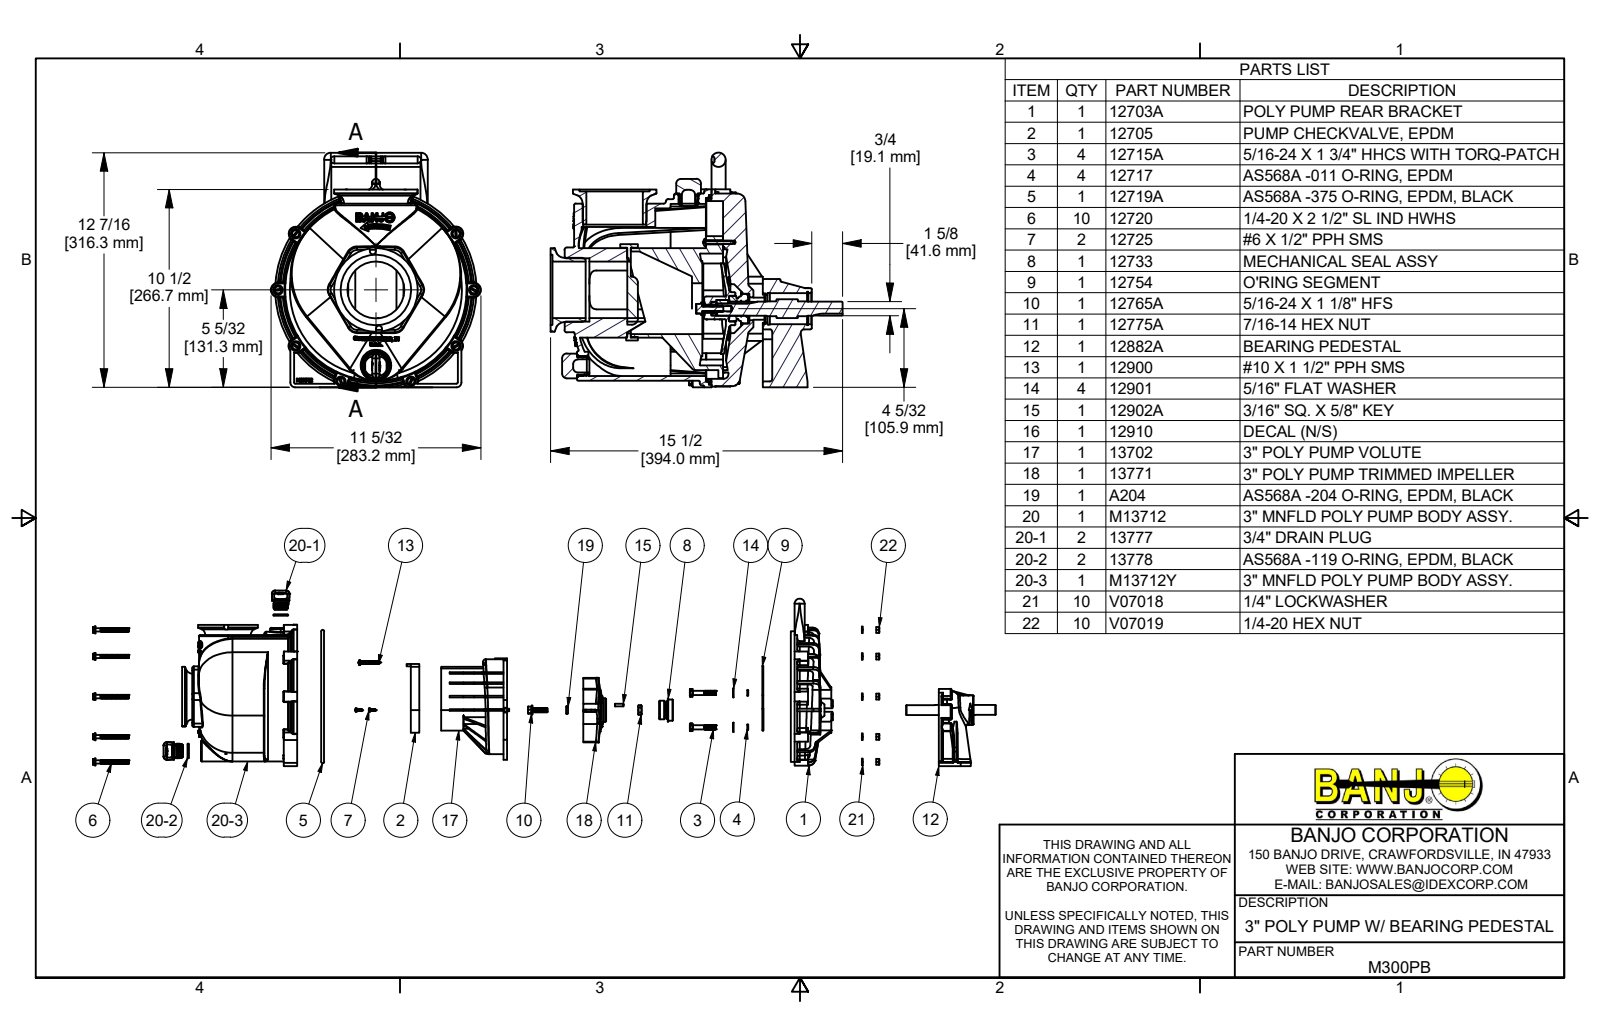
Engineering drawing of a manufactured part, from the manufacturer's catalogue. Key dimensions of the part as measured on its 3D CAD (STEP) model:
Part name (STEP PRODUCT): M300PB; 12703A; 12715A; 12717 (+8 more)
STEP written by: Autodesk Inventor 2019 (AUTOMOTIVE_DESIGN)
Units: inches
Bodies: 55 solids, 4980 faces (816 planar, 1578 cylindrical, 2586 other)
Overall size (bounding box): 12.417 × 11.15 × 4.35
Volume: 66.25 in³ · Surface area: 675 in²
Round holes (diameter × count): ⌀0.196 ×10, ⌀0.252 ×10, ⌀0.27 ×10, ⌀0.344 ×4, ⌀0.469 ×4, ⌀0.815 ×4, ⌀0.115 ×2, ⌀0.205 ×2, ⌀0.18 ×1, ⌀0.375 ×1, ⌀0.437 ×1, ⌀0.685 ×1
Round bosses / shafts (diameter × count): ⌀0.276 ×80, ⌀0.52 ×10, ⌀0.489 ×10, ⌀0.25 ×10, ⌀0.192 ×6, ⌀0.688 ×4, ⌀0.313 ×4, ⌀0.138 ×2
Partial cylindrical surfaces — rounded edges, fillets, slot ends (radius × count): R0.187 ×24, R0.25 ×21, R0.015 ×20, R0.125 ×11, R0.375 ×10, R0.138 ×8, R0.282 ×8, R0.062 ×7
Main face-to-face distances: 0.2, 1, 0.61, 0.41, 0.8, 0.39, 2.525, 0.198, 0.275, 0.885
Hole centre spacings: 5.2, 3.127, 6.15, 10.4, 1.81, 1.81, 2.559, 2.56
